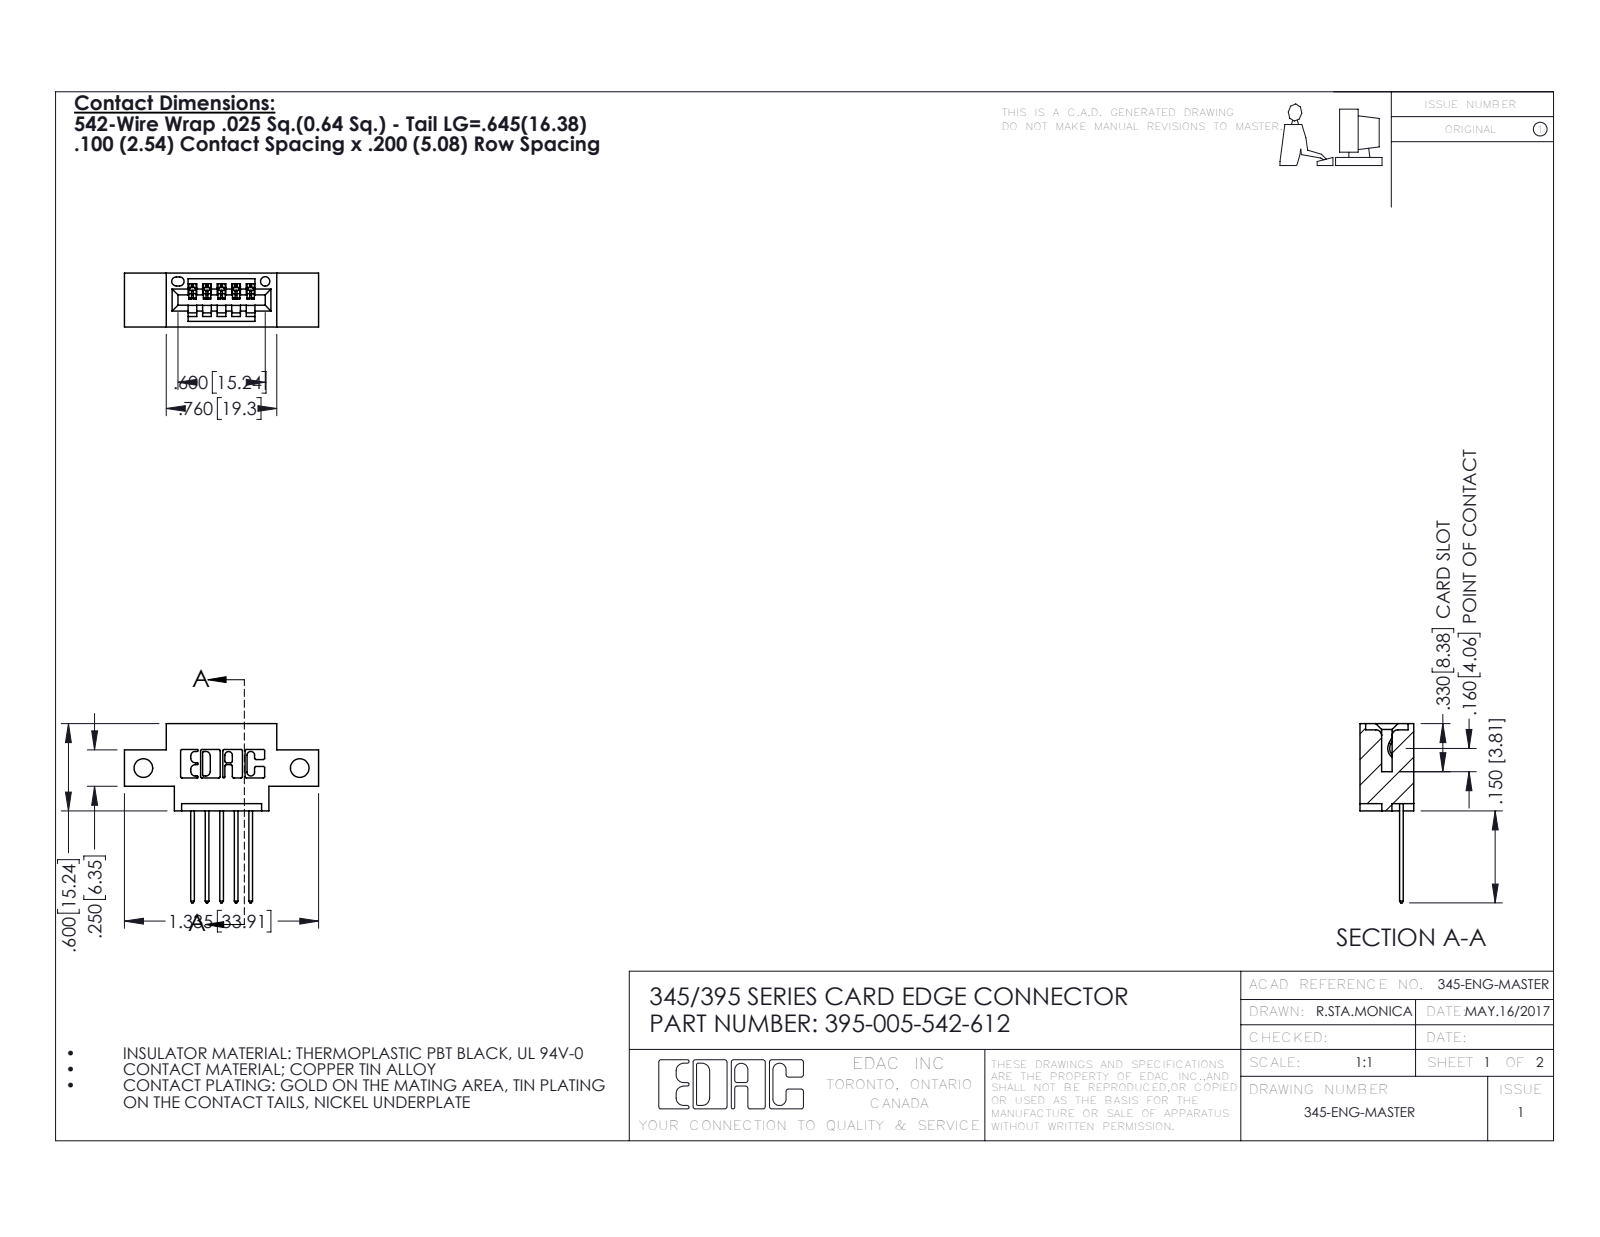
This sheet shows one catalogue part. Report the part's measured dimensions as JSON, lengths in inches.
{"part_name": "345-292-001_345-293-142; 345 Part_0.170 Offset - Side Mount; 395-005-542-612", "step_written_by": "SolidWorks 2016 (CONFIG_CONTROL_DESIGN)", "units": "inches", "bodies": {"solids": 6, "faces": 420, "planar": 284, "cylindrical": 136, "other": 0}, "overall_size": [1.335, 1.232, 0.37], "volume_in3": 0.166, "surface_area_in2": 4.925, "round_holes": [[0.128, 2], [0.064, 1]], "partial_cylinders_radius": [[0.01, 22], [0.006, 10], [0.01, 10], [0.007, 6], [0.031, 6], [0.026, 3], [0.031, 2], [0.04, 2]], "face_to_face_distances": [0.37, 0.2, 0.298, 0.072, 0.1, 0.025, 0.25, 0.098, 0.272, 0.06], "hole_center_spacings": [1.075]}
